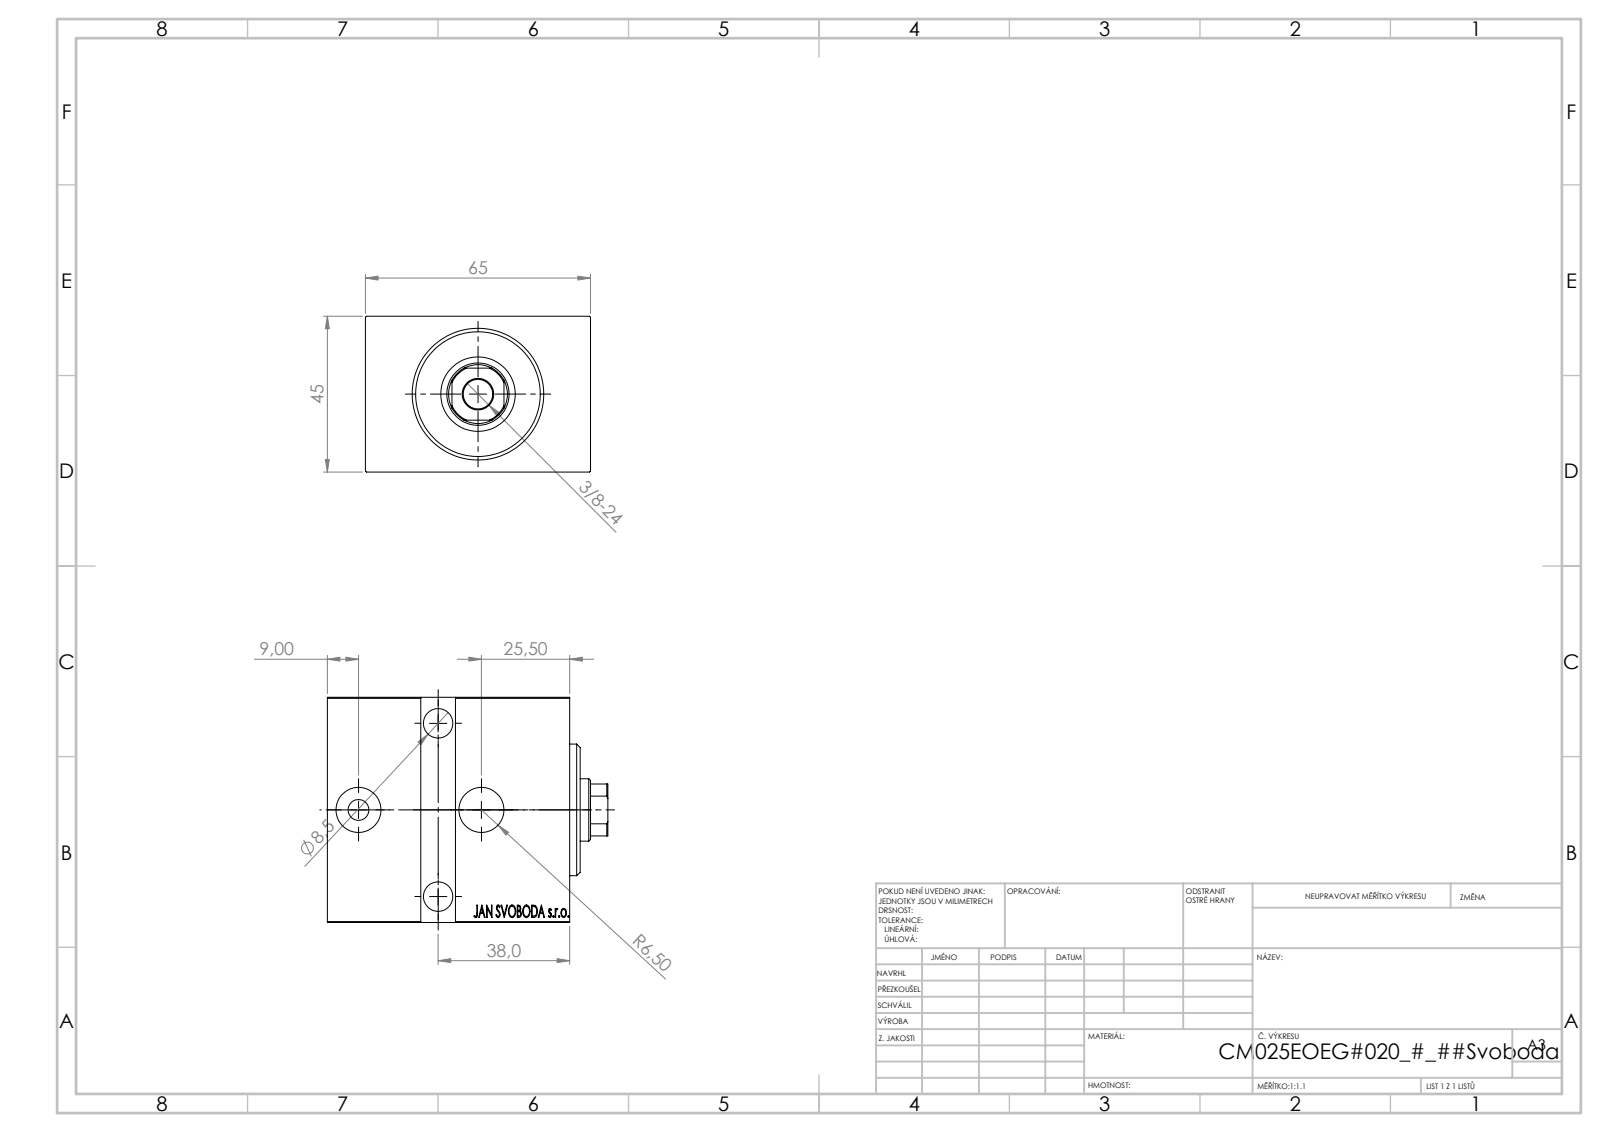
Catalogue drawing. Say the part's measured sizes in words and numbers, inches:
The part is named "V450CM_VC_B; V450CM_E_VCP; V450CM_E_Body". Its 3-D file was written by "SolidWorks 2019 (CONFIG_CONTROL_DESIGN)". It is 3 solids with 839 faces: 407 planar, 38 cylindrical and 394 other. Overall it measures 3.189 by 2.559 by 1.772 inches. Its volume is 11.9 cubic inches and its surface area 60.5 square inches. Round holes: 3 of diameter 0.335, 2 of diameter 0.512, 2 of diameter 0.531, 1 of diameter 0.709, 1 of diameter 0.846, 1 of diameter 0.984, 1 of diameter 1.378. Round bosses or shafts: 1 of diameter 1.496, 1 of diameter 1.063, 1 of diameter 0.236. Partial cylindrical surfaces (rounded edges, fillets, slot ends): 1 of radius 0.335. The main face-to-face distances are 2.559, 1.772, 2.756, 0.315, 0.118, 0.236, 2.52, 0.197, 2.323, 1.693. The hole center spacings are 1.1, 1.337, 1.398, 1.969.
